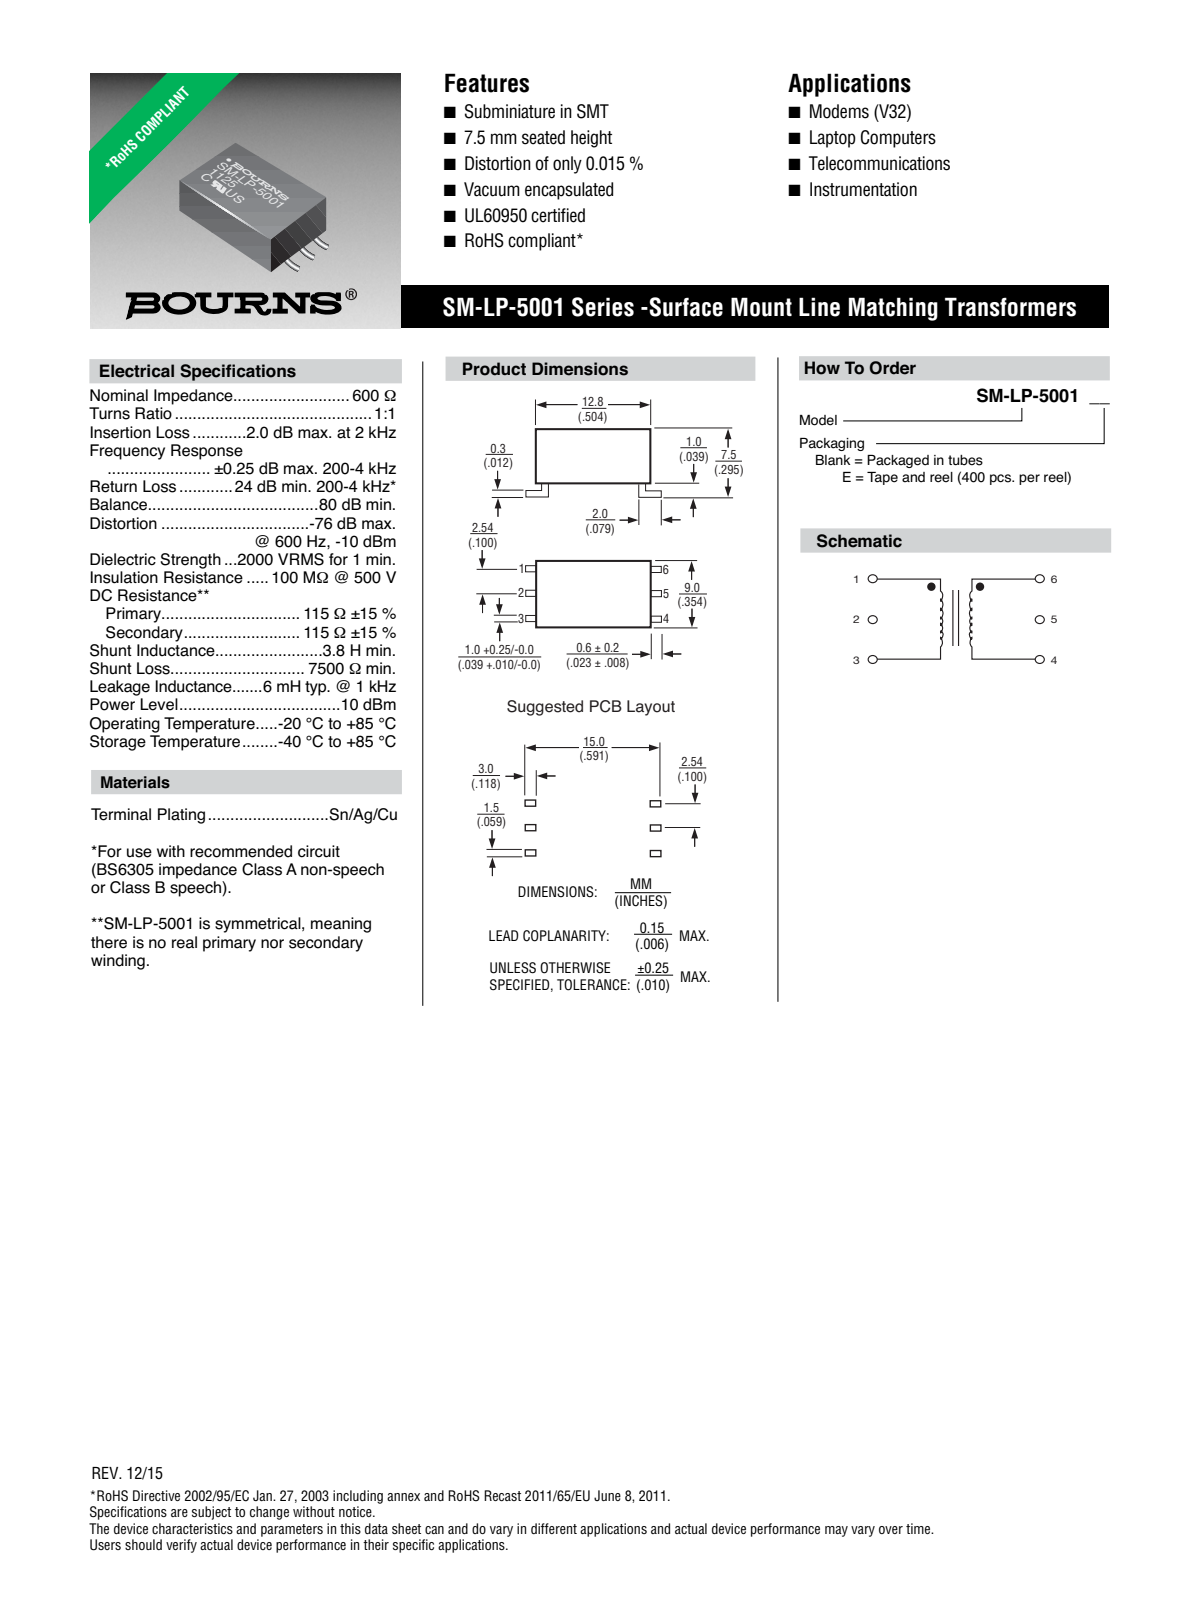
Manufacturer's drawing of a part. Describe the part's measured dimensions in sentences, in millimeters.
The part is named "SM-LP-5001". Its 3-D file was written by "PRO/ENGINEER BY PARAMETRIC TECHNOLOGY CORPORATION, 2010100 (CONFIG_CONTROL_DESIGN)". It is 1 solid with 60 faces: 48 planar, 12 cylindrical and 0 other. Overall it measures 14 by 9.35 by 7.36 millimeters. Its volume is 766 cubic millimeters and its surface area 562 square millimeters. Partial cylindrical surfaces (rounded edges, fillets, slot ends): 4 of radius 0.2. The main face-to-face distances are 6.36, 9.34, 12.8, 1, 7.36, 0.7, 7.06, 2.54, 1.4, 11.4.
